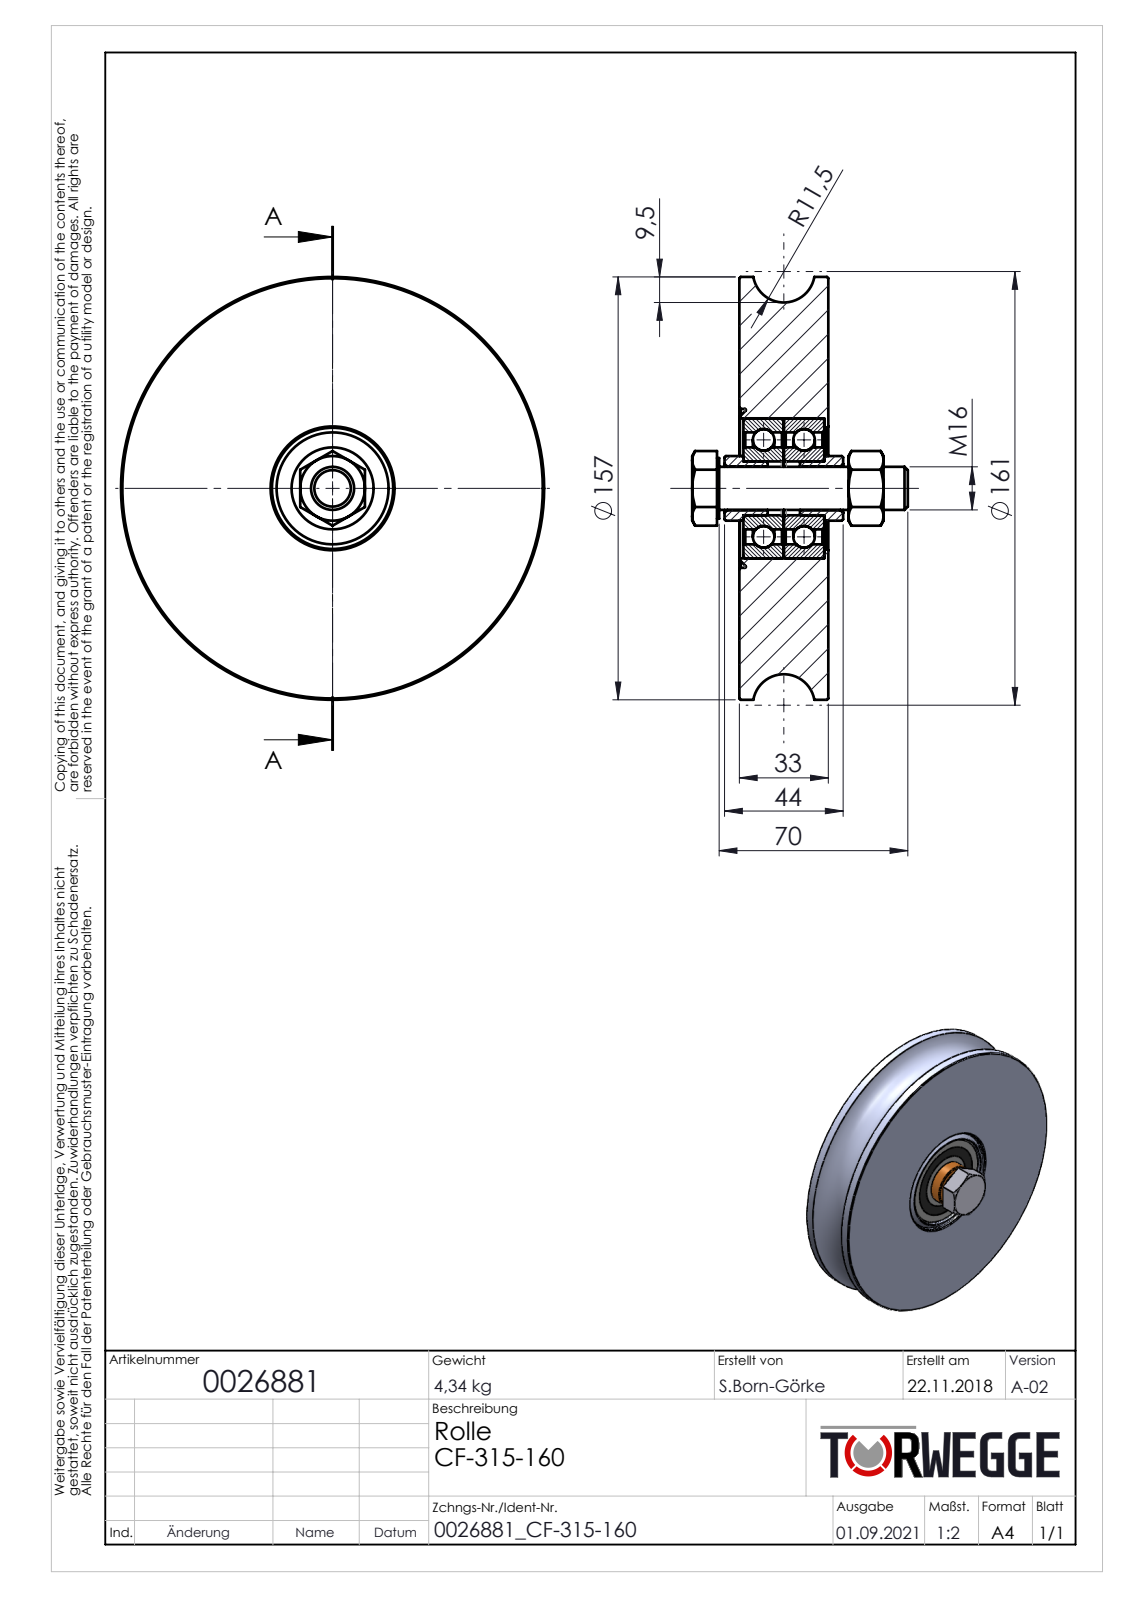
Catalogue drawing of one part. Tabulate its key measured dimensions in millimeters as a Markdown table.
| quantity | value |
| --- | --- |
| part name | 0026881 |
| STEP written by | SolidWorks 2020 (AUTOMOTIVE_DESIGN) |
| units | millimeters |
| bodies | 0 solids, 92 faces (26 planar, 26 cylindrical, 40 other) |
| overall size | 157 × 157 × 80 |
| round holes (diameter × count) | 41.56 × 1, 45 × 1, 52 × 1, 59 × 1 |
| round bosses / shafts (diameter × count) | 157 × 1, 30.44 × 1, 24 × 1, 22.5 × 1, 16 × 1 |
| main face-to-face distances | 33, 1.5, 31.5, 1.7, 31.3, 29.8, 30, 24, 29.6, 17.5 |
